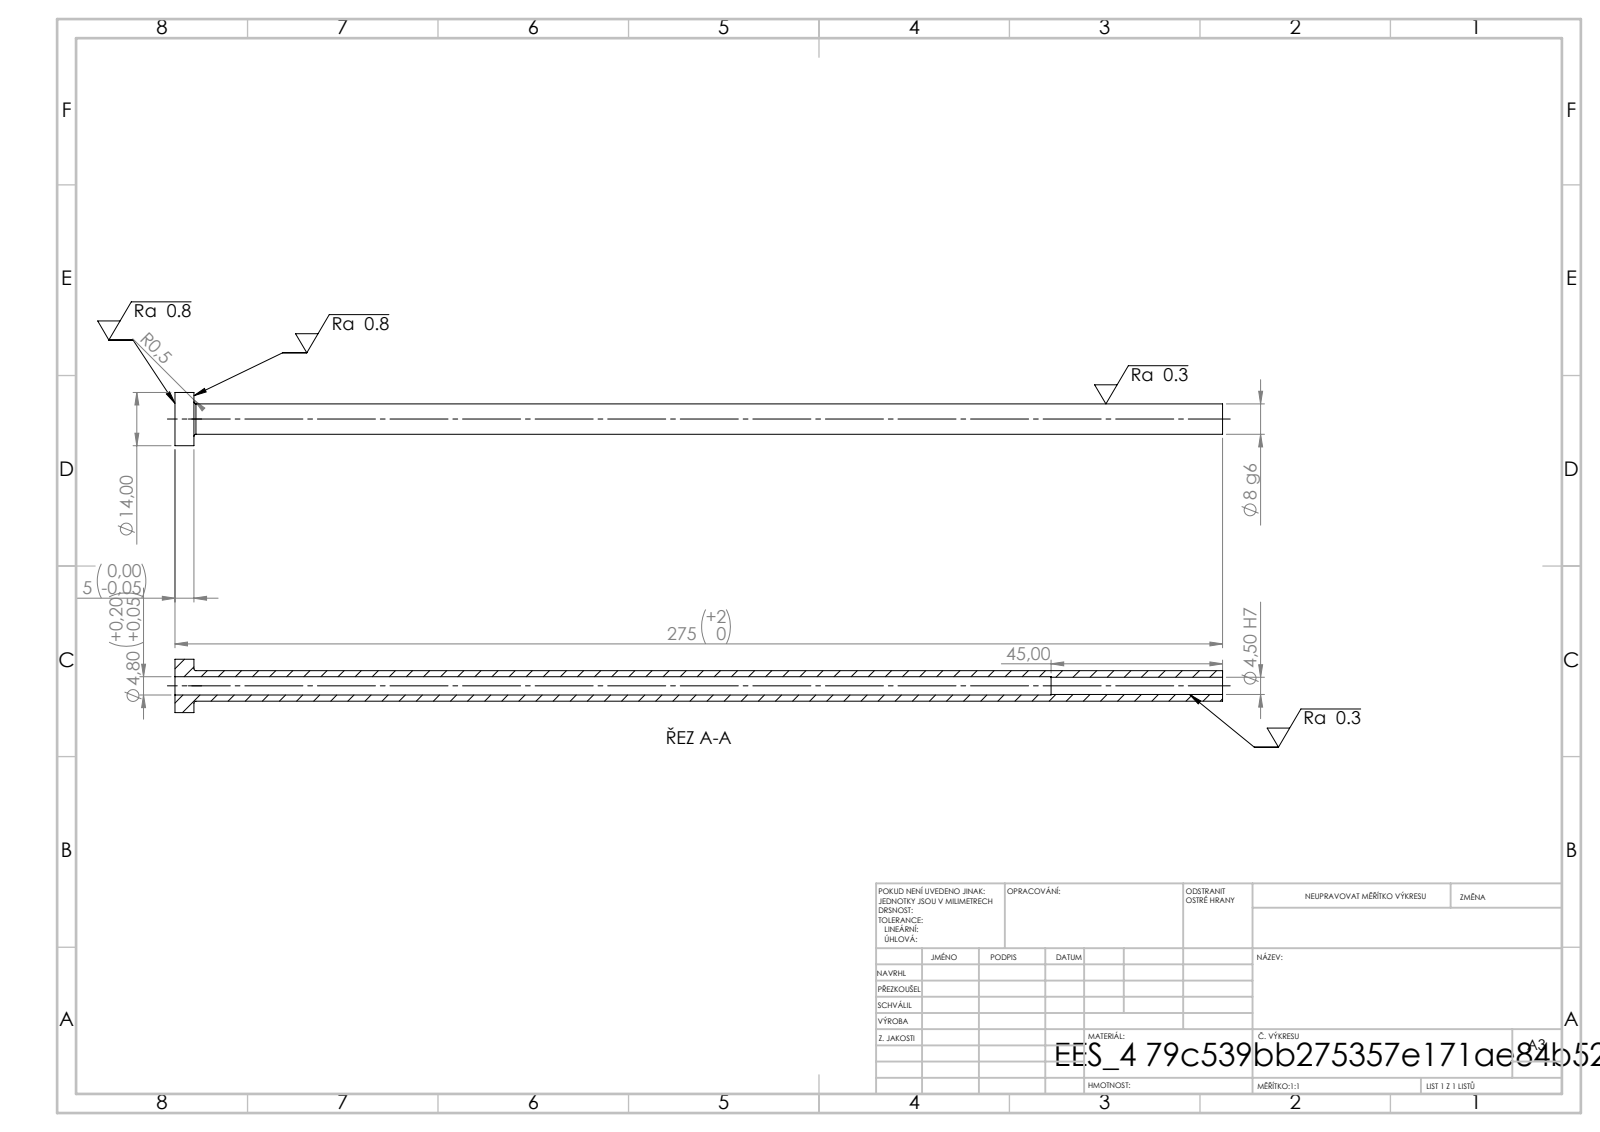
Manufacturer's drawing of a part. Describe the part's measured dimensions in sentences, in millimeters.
Its 3-D file was written by "SolidWorks 2019 (CONFIG_CONTROL_DESIGN)". It is 1 solid with 14 faces: 4 planar, 8 cylindrical and 2 other. Overall it measures 275 by 14 by 14 millimeters. Its volume is 9 465 cubic millimeters and its surface area 11 381 square millimeters. Round holes: 1 of diameter 4.5, 1 of diameter 4.8. Round bosses or shafts: 1 of diameter 14, 1 of diameter 8. The main face-to-face distances are 5, 275, 270, 230, 225, 45.
